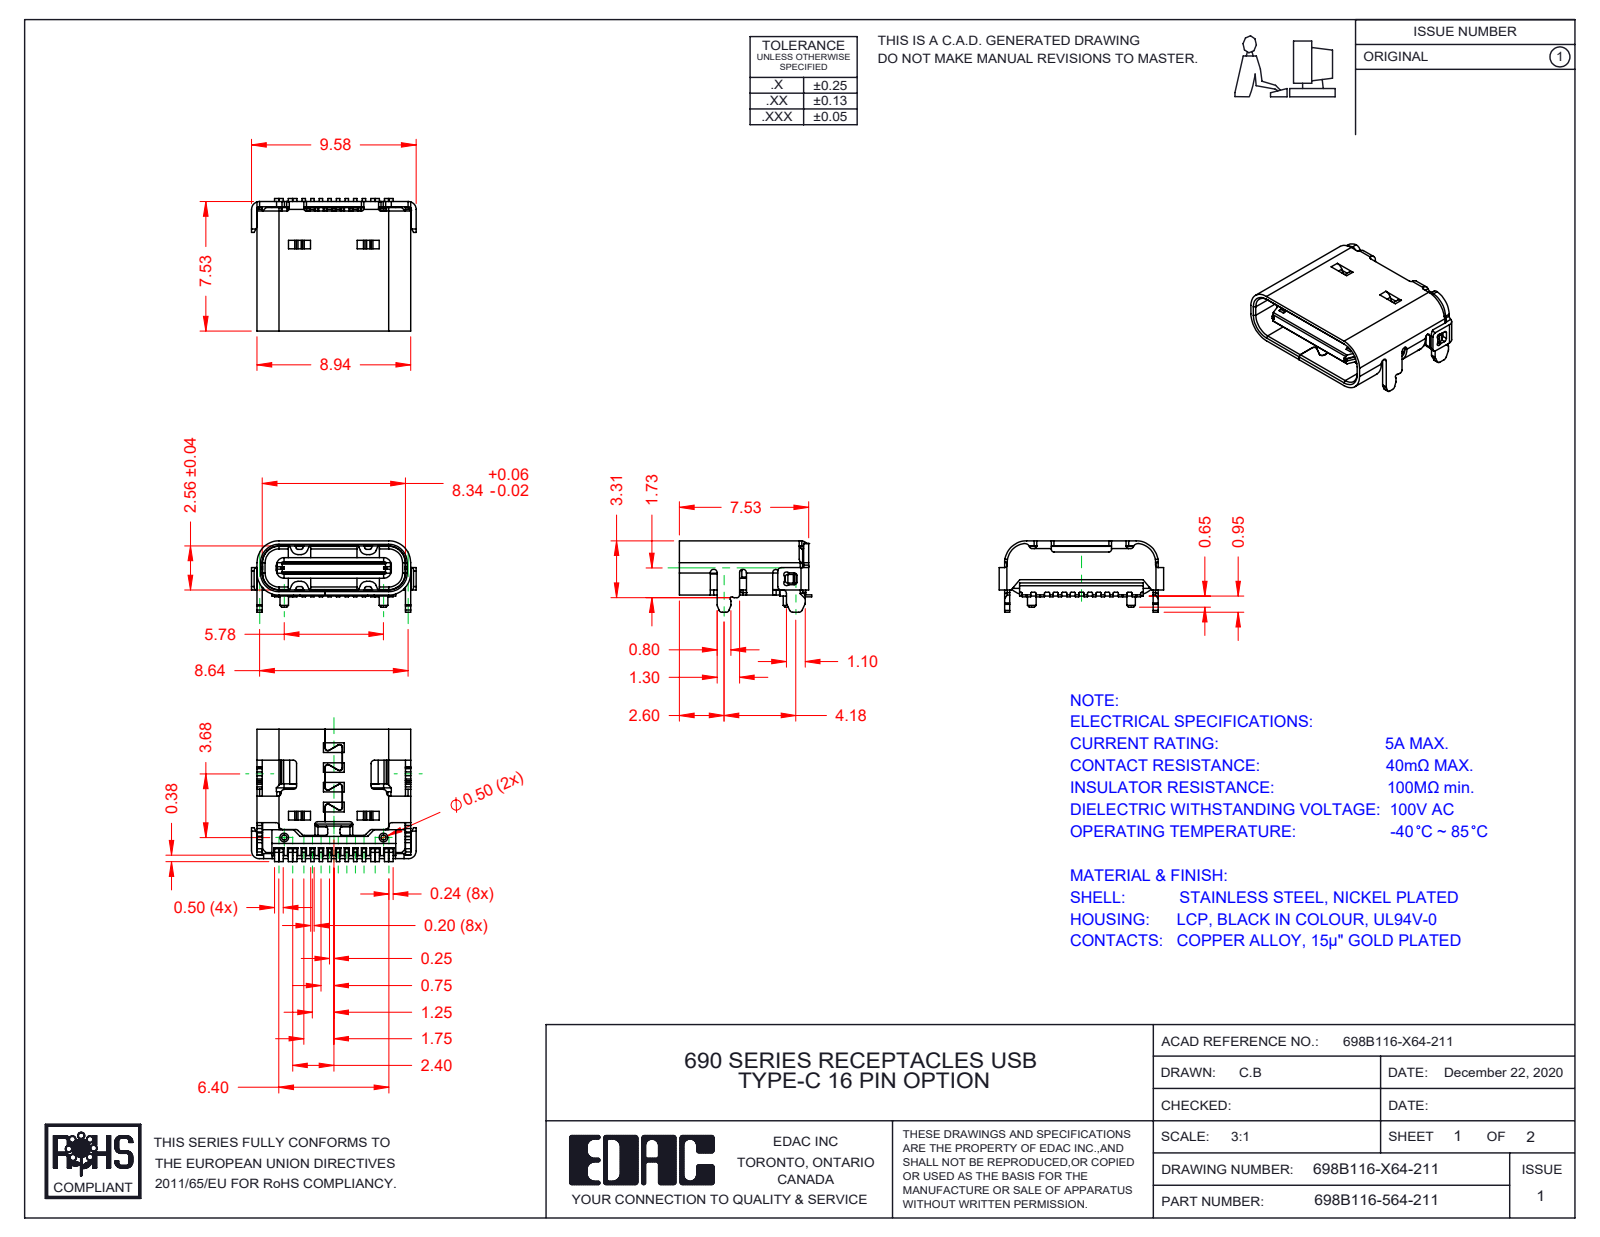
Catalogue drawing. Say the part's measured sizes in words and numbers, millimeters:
The part is named "Contacts 698B116-X64-211; Insulator 698B116-X64-211; 698B116-164-211; Shell 698B116-X64-211". Its 3-D file was written by "SolidWorks 2020 (AUTOMOTIVE_DESIGN)". It is 22 solids with 1997 faces: 1414 planar, 541 cylindrical and 42 other. Overall it measures 9.58 by 7.71 by 4.16 millimeters. Its volume is 116 cubic millimeters and its surface area 712 square millimeters. Round bosses or shafts: 2 of diameter 0.5. Partial cylindrical surfaces (rounded edges, fillets, slot ends): 76 of radius 0.15, 53 of radius 0.2, 51 of radius 0.1, 16 of radius 0.4, 15 of radius 0.13, 14 of radius 0.17, 11 of radius 0.45, 8 of radius 0.16. The main face-to-face distances are 2.86, 0.66, 1.89, 1.59, 0.97, 1.27, 1.93, 0.93, 1.23, 1.63.
